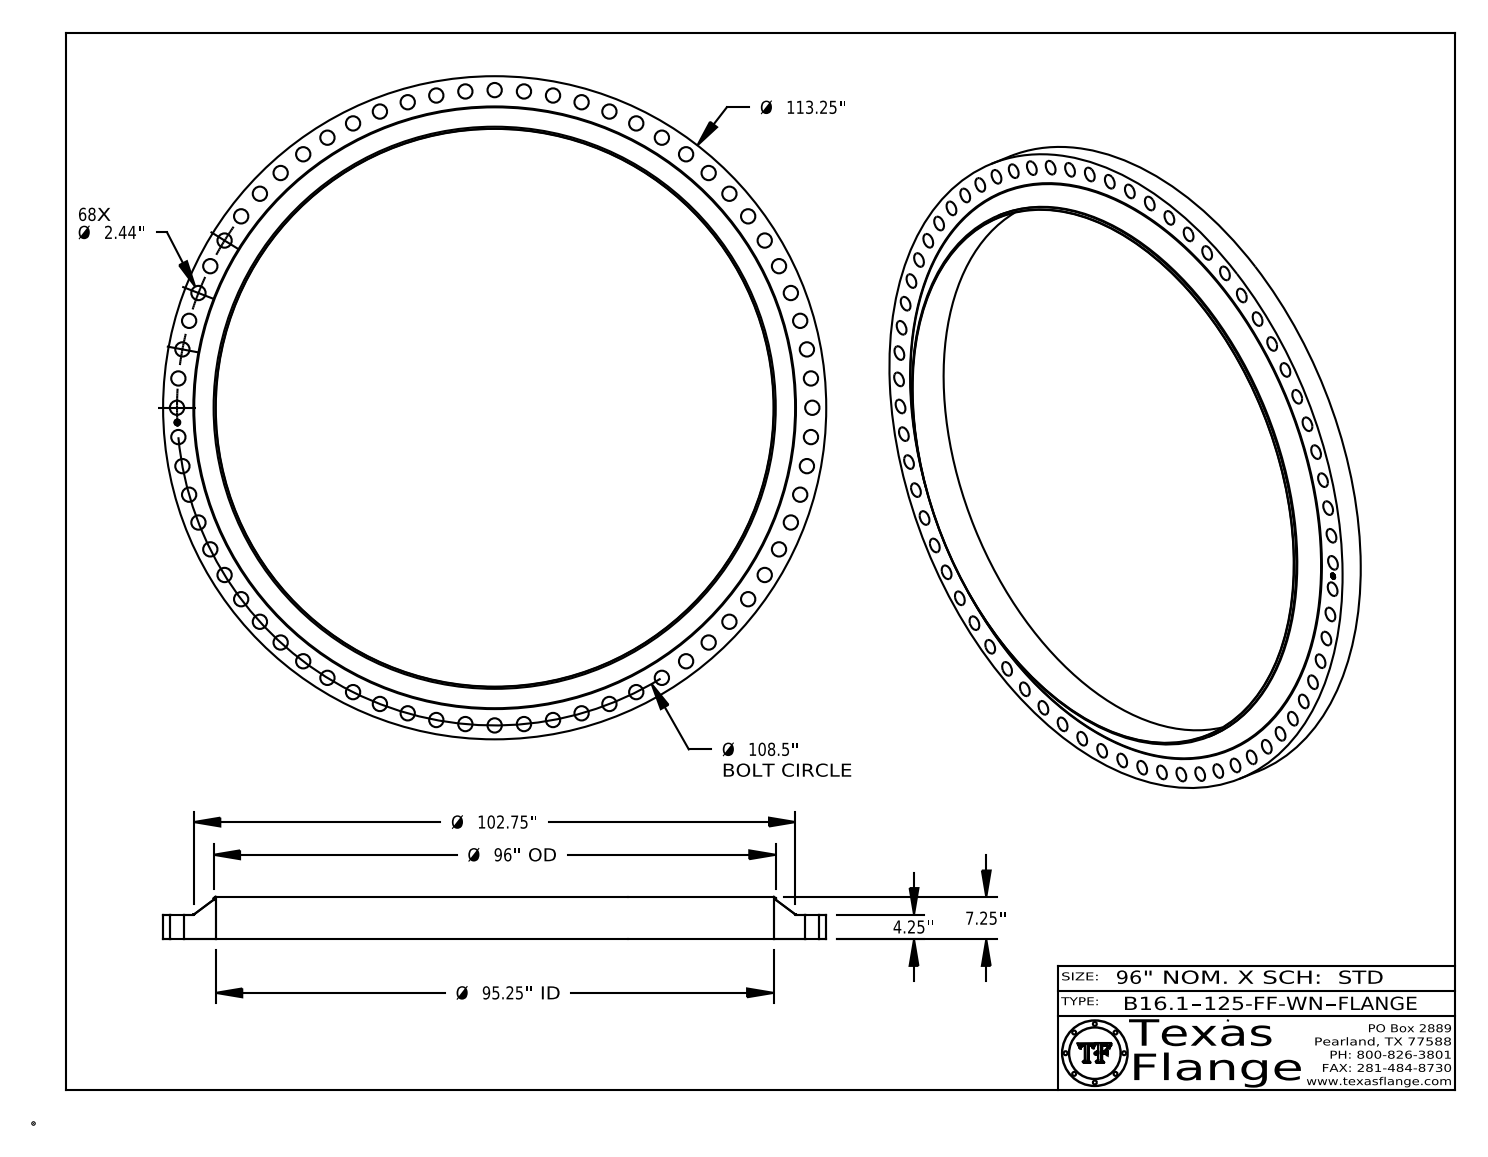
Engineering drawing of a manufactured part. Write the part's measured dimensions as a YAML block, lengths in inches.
part_name: "B16.1, Class 125-FF-WN"
step_written_by: "CATIA V5 STEP AP214 (AUTOMOTIVE_DESIGN)"
units: inches
bodies: {solids: 1, faces: 536, planar: 368, cylindrical: 162, other: 6}
overall_size: [113.25, 113.25, 7.25]
volume: 12818
surface_area: 11512
round_holes:
  - {diameter: 2.44, count: 68}
  - {diameter: 1, count: 1}
  - {diameter: 95.25, count: 1}
round_bosses_or_shafts:
  - {diameter: 0.061, count: 8}
  - {diameter: 113.25, count: 1}
  - {diameter: 96, count: 1}
  - {diameter: 0.788, count: 1}
face_to_face_distances: [4.25, 7.25, 3, 4.235, 0.015, 3.015, 0.298, 0.293, 0.054, 0.193]
hole_center_spacings: [54.25, 108.037, 106.653, 108.384, 14.99, 105.618, 19.937, 5.011]
